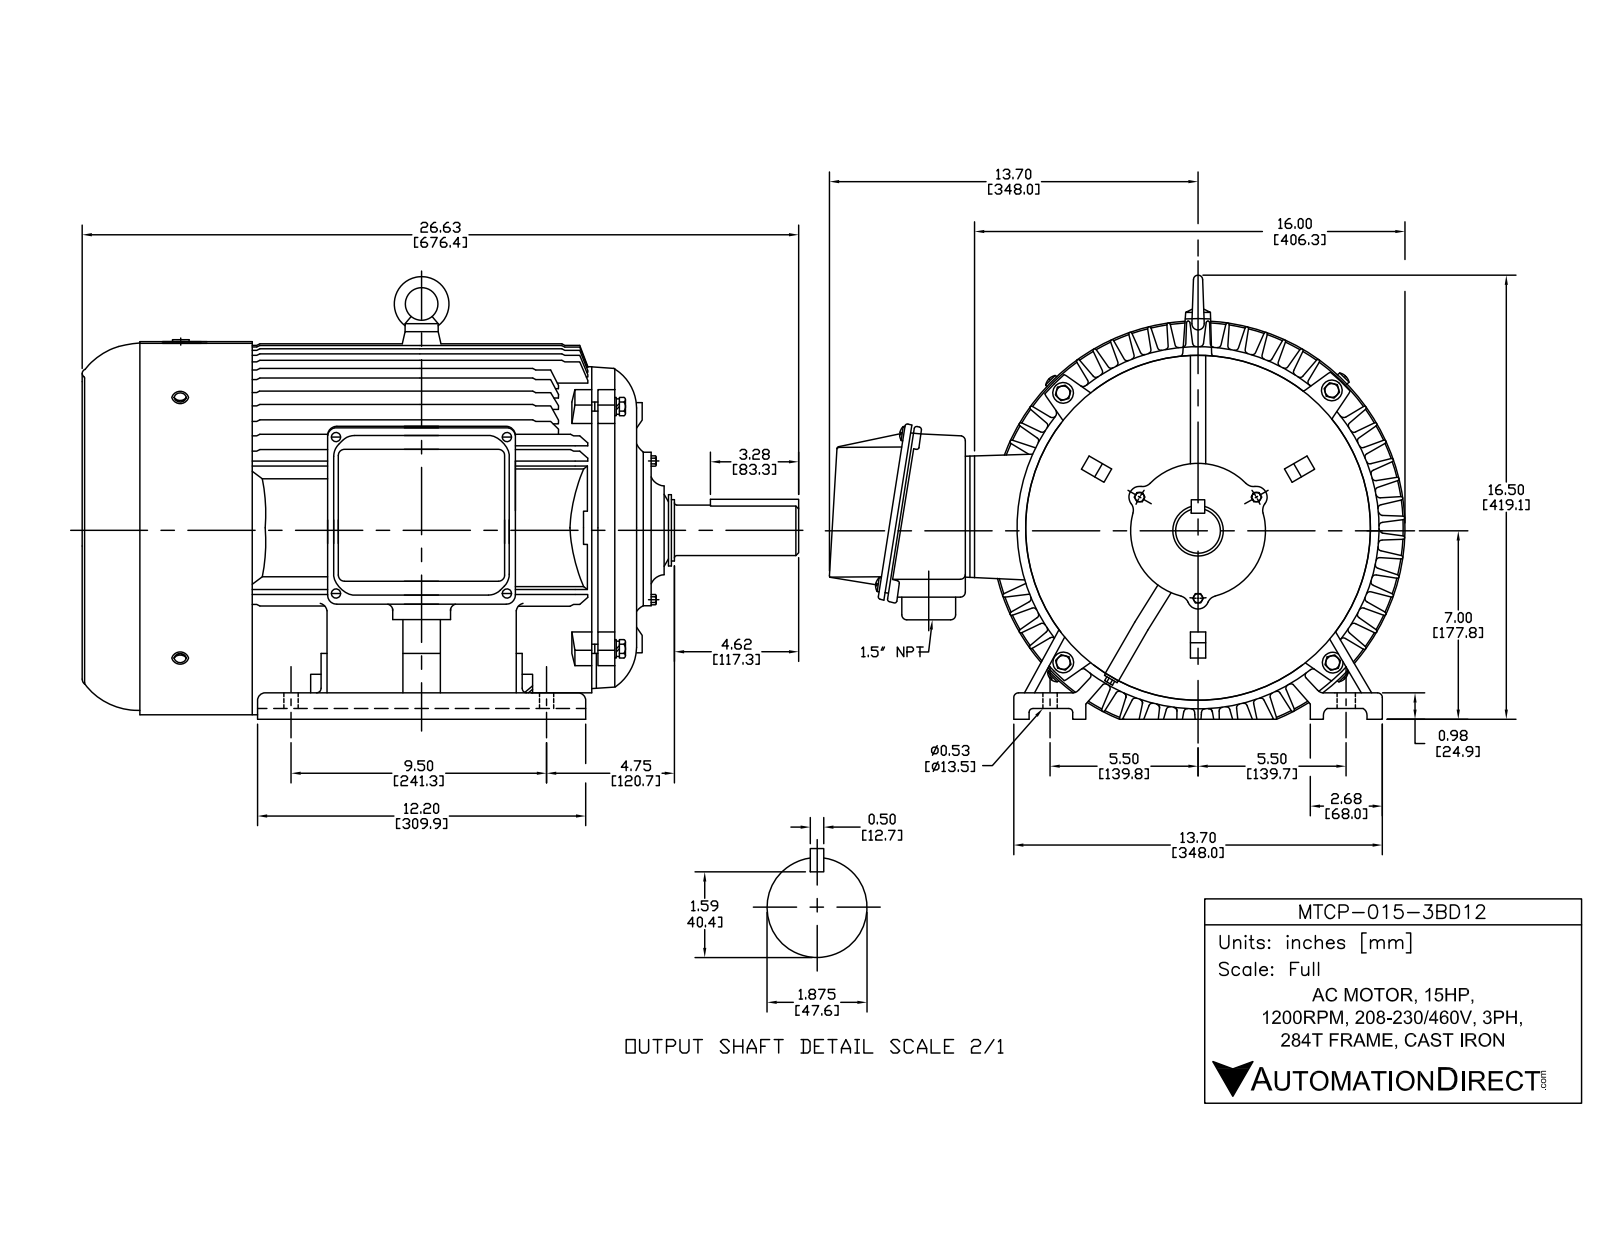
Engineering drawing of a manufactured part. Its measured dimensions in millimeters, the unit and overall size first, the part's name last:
Units: millimetres
Overall size (bounding box): 681.5 × 489.93 × 443
Round holes (diameter × count): ⌀7 ×14, ⌀10 ×10, ⌀5 ×8, ⌀6.4 ×4, ⌀6.68 ×4, ⌀6.8 ×4, ⌀8.5 ×4, ⌀9 ×4, ⌀10.2 ×4, ⌀11.39 ×4, ⌀12.9 ×4, ⌀13 ×4
Round bosses / shafts (diameter × count): ⌀12 ×8, ⌀6 ×8, ⌀8 ×6, ⌀24 ×4, ⌀19.1 ×4, ⌀9.88 ×4, ⌀5 ×4, ⌀10 ×2
Partial cylindrical surfaces — rounded edges, fillets, slot ends (radius × count): R1 ×265, R5 ×78, R3 ×76, R0.5 ×48, R1.5 ×36, R0.75 ×24, R10 ×24, R8 ×18
Main face-to-face distances: 1.5, 5, 20, 520.5, 519, 40, 8.5, 529, 527.5, 60
Hole centre spacings: 144, 100, 65, 70, 116.94, 213.78, 67.64, 5
Volume: 10 740 000 mm³ · Surface area: 3 002 000 mm²
Bodies: 68 solids, 3872 faces (1106 planar, 1427 cylindrical, 1339 other)
Part name (STEP PRODUCT): hexagon head bolts-full thread gb_GB_FASTENER_BOLT_STBAB A M8X50-N; hex head bolts-full thread grade c gb_GB_FASTENER_BOLT_HHBFTC M5X16-N; PE280前轴承外盖加工件; eyebolts gb_GB_FASTENER_SCREWS_FRS M16-N (+8 more)
STEP written by: SolidWorks 2017 (AUTOMOTIVE_DESIGN)
